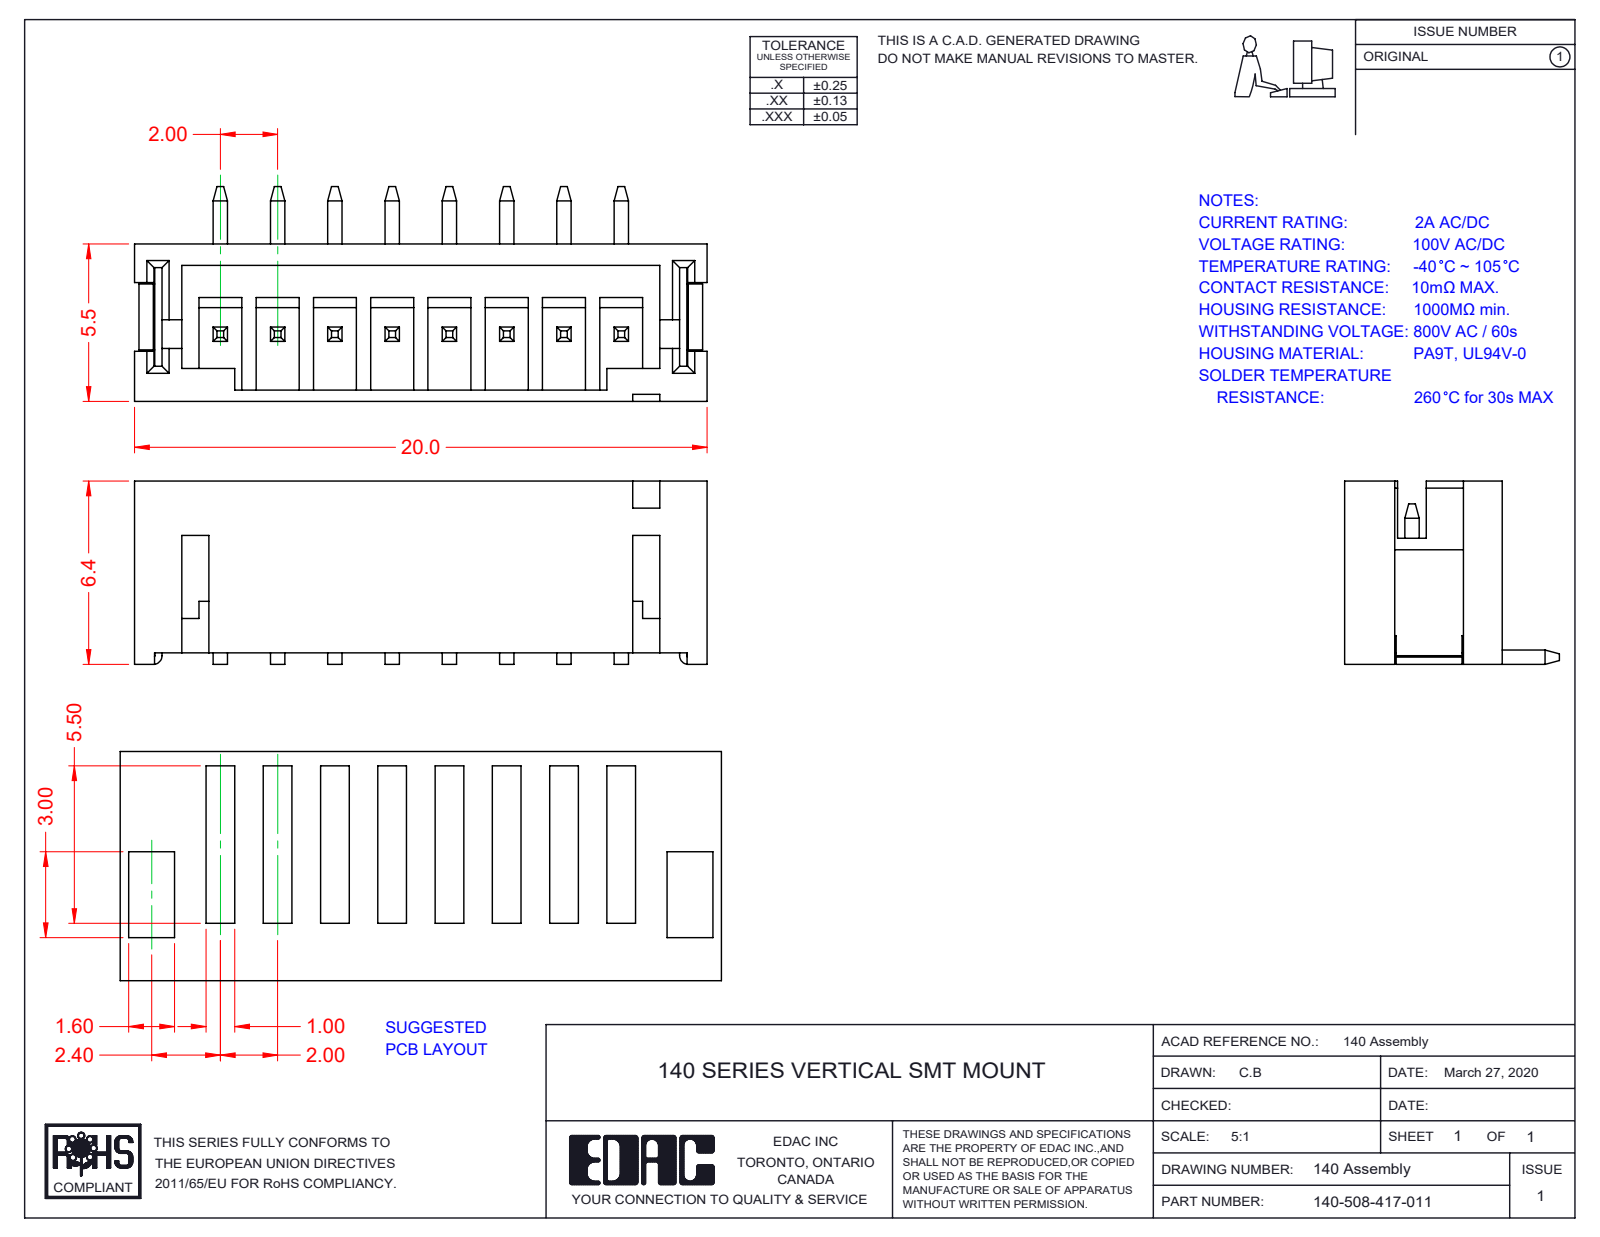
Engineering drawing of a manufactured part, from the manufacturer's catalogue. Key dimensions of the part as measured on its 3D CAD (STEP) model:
Part name (STEP PRODUCT): V SMT Pad; 140-508-417-011; V SMT Contact; V SMT Housing_508
STEP written by: SolidWorks 2016 (CONFIG_CONTROL_DESIGN)
Units: millimetres
Bodies: 11 solids, 404 faces (384 planar, 20 cylindrical, 0 other)
Overall size (bounding box): 20 × 7.5 × 6.4
Volume: 300 mm³ · Surface area: 1 080 mm²
Partial cylindrical surfaces — rounded edges, fillets, slot ends (radius × count): R0.3 ×2, R0.55 ×1
Main face-to-face distances: 5.5, 0.75, 4.75, 0.4, 0.5, 4.35, 5.1, 0.6, 6, 0.55
